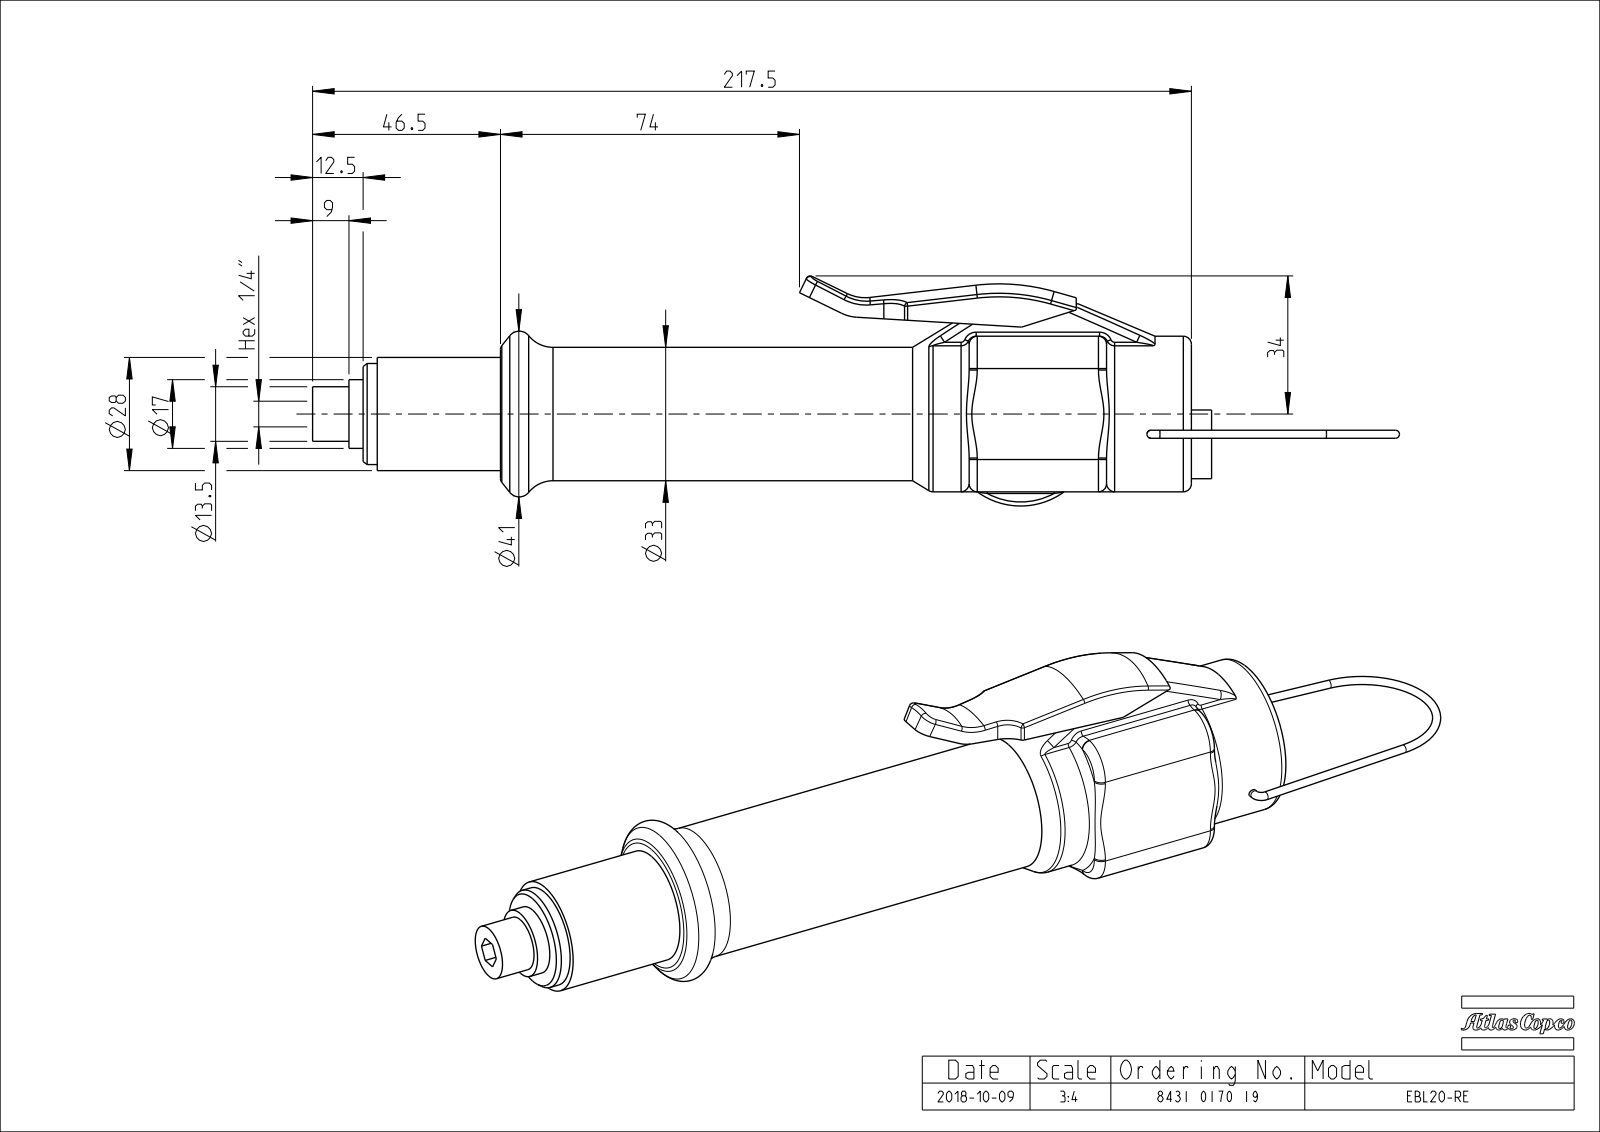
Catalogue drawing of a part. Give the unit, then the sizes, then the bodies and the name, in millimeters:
Units: millimetres
Overall size (bounding box): 269 × 56.91 × 45
Round holes (diameter × count): ⌀14.5 ×1
Round bosses / shafts (diameter × count): ⌀2 ×5, ⌀17 ×2, ⌀38.5 ×1, ⌀33 ×1, ⌀28 ×1, ⌀25 ×1, ⌀13.5 ×1
Partial cylindrical surfaces — rounded edges, fillets, slot ends (radius × count): R1 ×10, R0.4 ×6, R2 ×4, R8 ×4, R20.43 ×3, R3 ×2, R7.74 ×2, R10 ×1
Main face-to-face distances: 40.5, 10.25, 30.25, 11.5, 20, 29, 34, 12.5, 1.25, 18.75
Volume: 214 260 mm³ · Surface area: 31 343 mm²
Bodies: 1 solid, 246 faces (58 planar, 69 cylindrical, 119 other)
Part name (STEP PRODUCT): 8431017011; 8431017019_DIM_ASM
STEP written by: CREO PARAMETRIC BY PTC INC, 2018100 (CONFIG_CONTROL_DESIGN)
